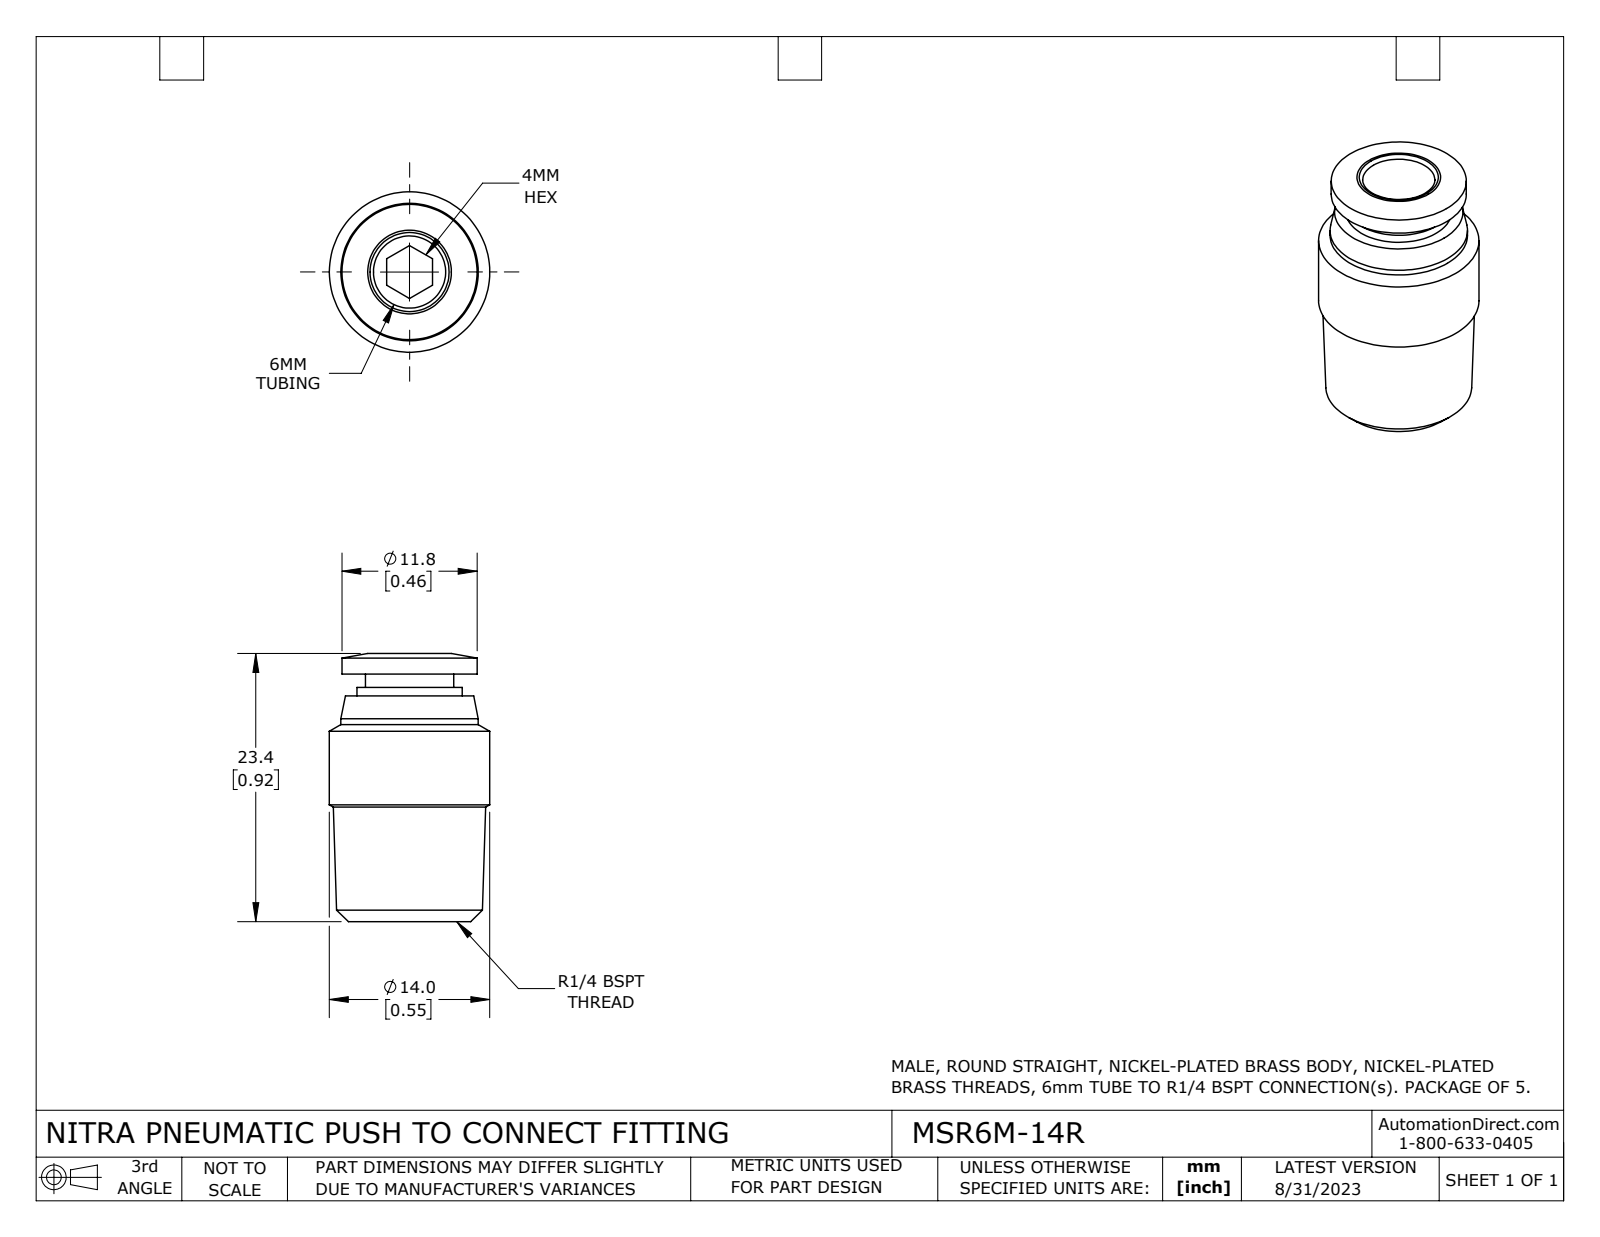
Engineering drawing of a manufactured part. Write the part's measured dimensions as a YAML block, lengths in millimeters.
part_name: "MSR6M-14R"
step_written_by: "SolidWorks 2015 (AUTOMOTIVE_DESIGN)"
units: millimeters
bodies: {solids: 1, faces: 34, planar: 6, cylindrical: 14, other: 14}
overall_size: [23.4, 14, 14]
volume: 2360
surface_area: 1662
round_holes:
  - {diameter: 4, count: 1}
  - {diameter: 6.3, count: 1}
round_bosses_or_shafts:
  - {diameter: 14, count: 1}
  - {diameter: 12, count: 1}
  - {diameter: 11.8, count: 1}
  - {diameter: 9.2, count: 1}
  - {diameter: 7.7, count: 1}
face_to_face_distances: [21.6, 19.7, 1.9, 20.4, 0.8, 1.1, 7, 12.7, 13.5, 14.6]
